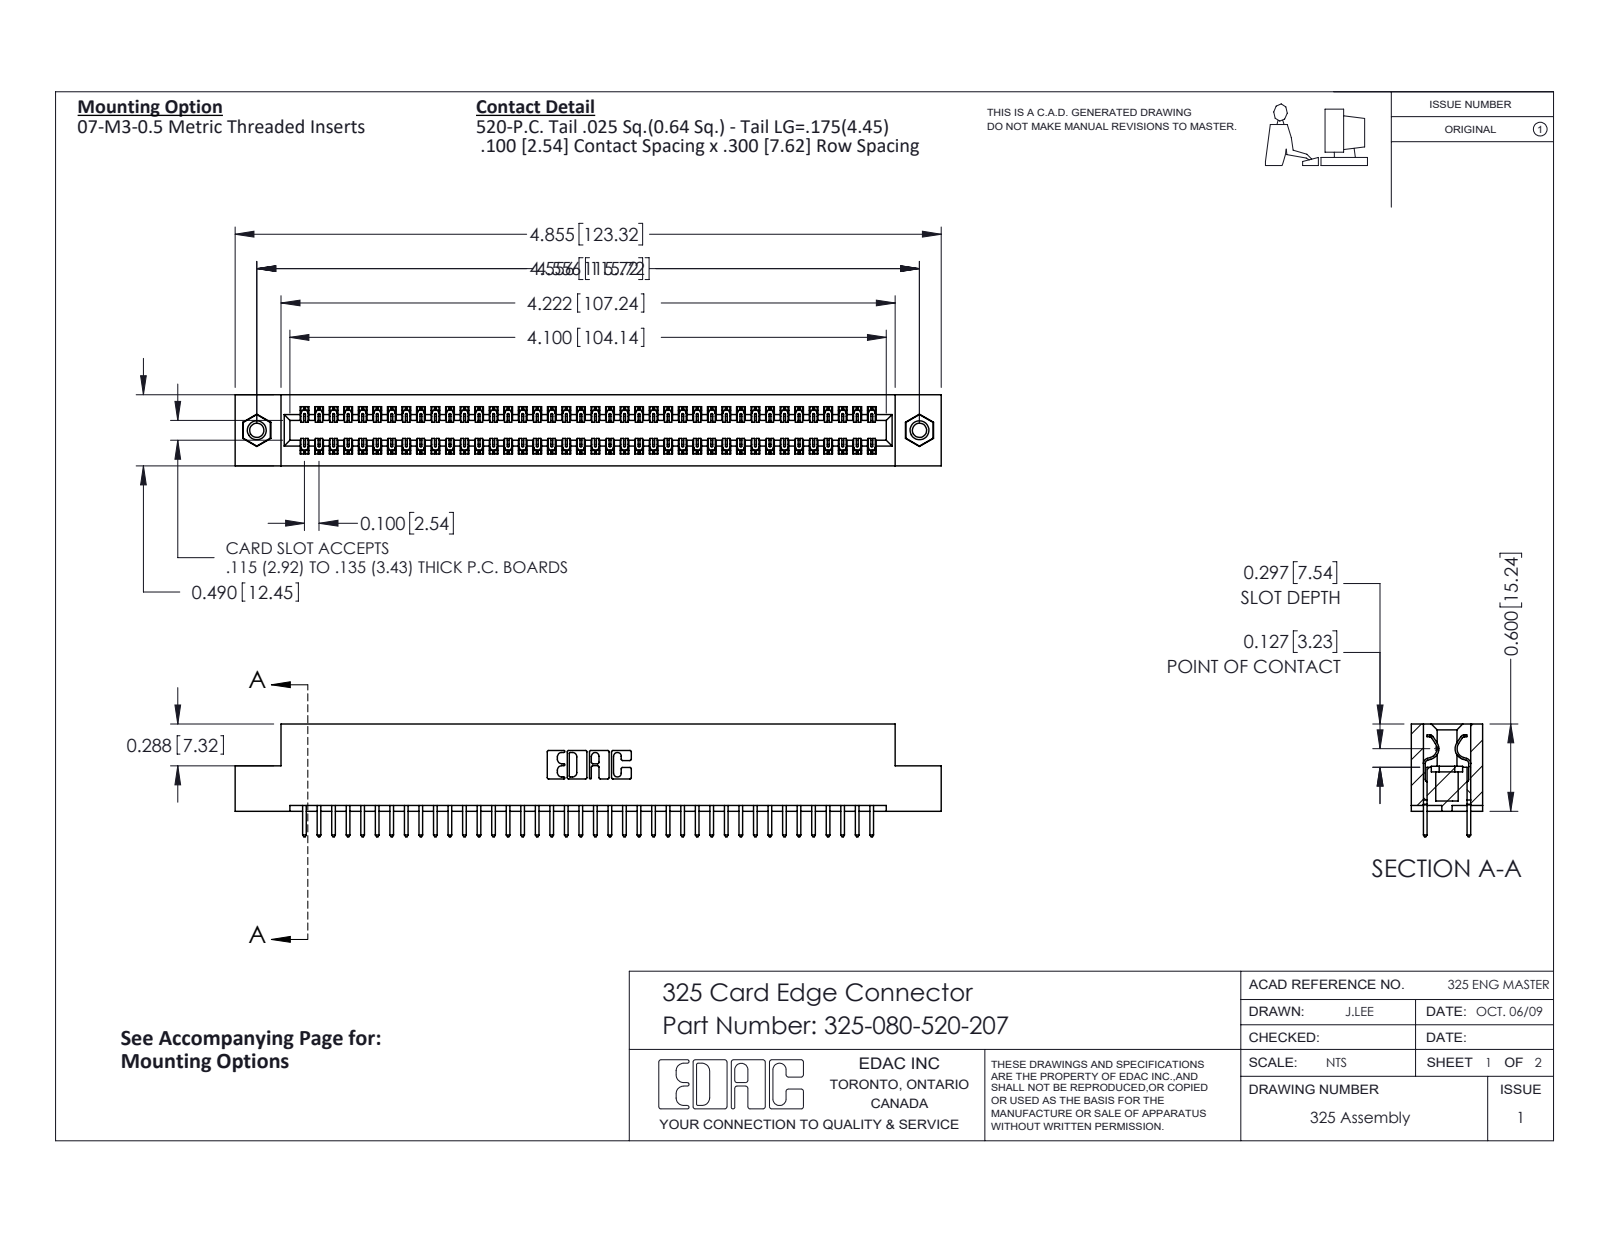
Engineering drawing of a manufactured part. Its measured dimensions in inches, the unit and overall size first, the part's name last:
Units: inches
Overall size (bounding box): 4.855 × 0.775 × 0.49
Round holes (diameter × count): ⌀0.098 ×2, ⌀0.125 ×2, ⌀0.16 ×2
Round bosses / shafts (diameter × count): ⌀0.155 ×2
Partial cylindrical surfaces — rounded edges, fillets, slot ends (radius × count): R0.006 ×120, R0.01 ×80, R0.01 ×22, R0.007 ×6, R0.031 ×6, R0.026 ×3, R0.014 ×2, R0.022 ×2
Main face-to-face distances: 0.083, 0.407, 0.49, 0.3, 0.107, 0.383, 0.025, 0.325, 0.275, 0.56
Hole centre spacings: 4.556
Volume: 0.969 in³ · Surface area: 29.5 in²
Bodies: 83 solids, 4334 faces (2982 planar, 1336 cylindrical, 16 other)
Part name (STEP PRODUCT): 325 Part_TI; 345-250-001_345-250-005-103; 325-292-001_325-293-120; 325-080-520-207
STEP written by: SolidWorks 2016 (CONFIG_CONTROL_DESIGN)
